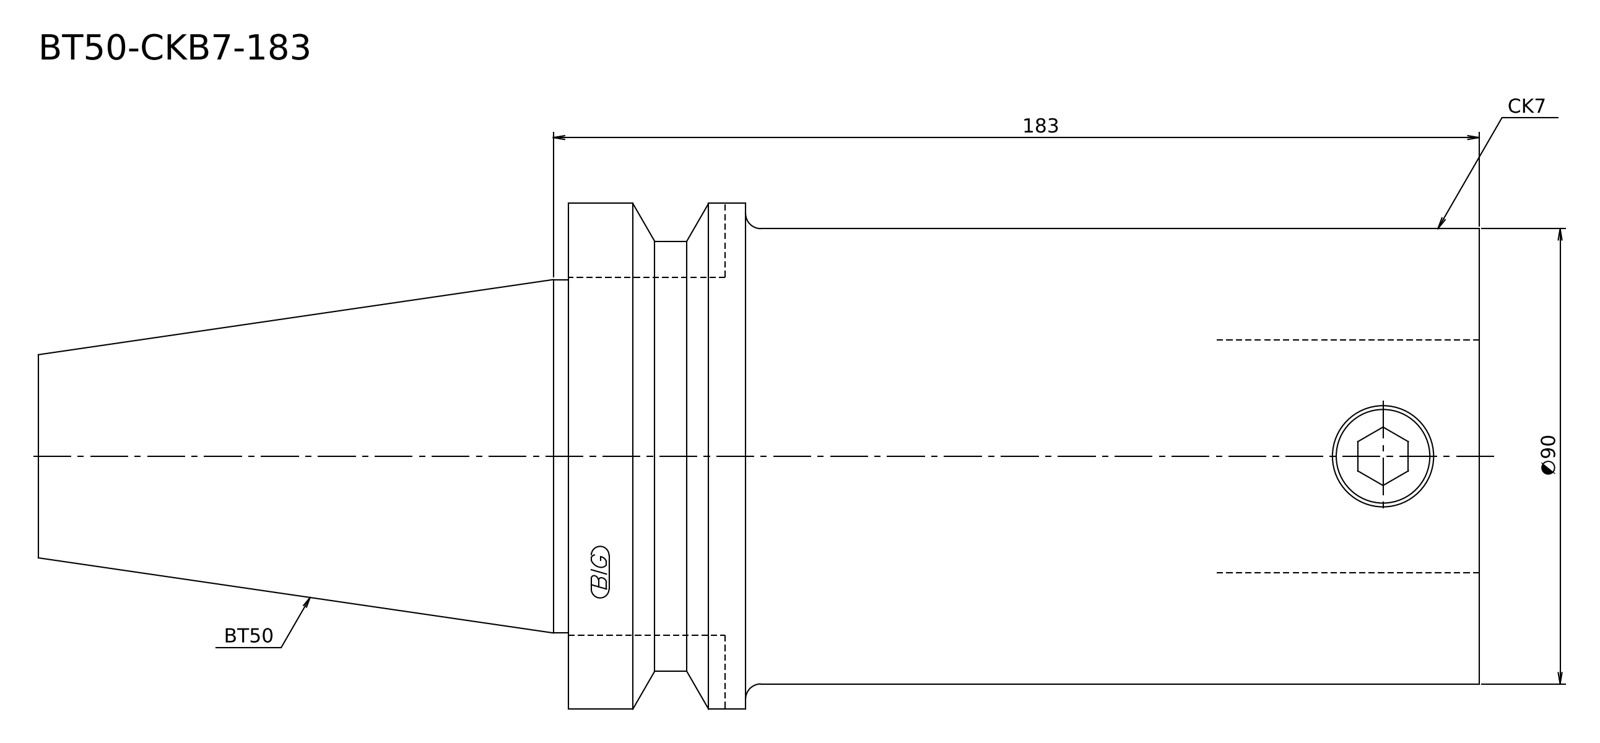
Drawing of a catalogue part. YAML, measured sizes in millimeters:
step_written_by: "Kubotek KeyCreator V8.5.1 (14335) (CONFIG_CONTROL_DESIGN)"
units: millimeters
bodies: {solids: 1, faces: 13, planar: 4, cylindrical: 5, other: 4}
overall_size: [284.8, 100, 100]
volume: 1434000
surface_area: 85100
round_bosses_or_shafts:
  - {diameter: 100, count: 1}
  - {diameter: 90, count: 1}
  - {diameter: 85, count: 1}
  - {diameter: 69.85, count: 1}
face_to_face_distances: [180, 284.8, 104.8, 145, 35, 139.8]
